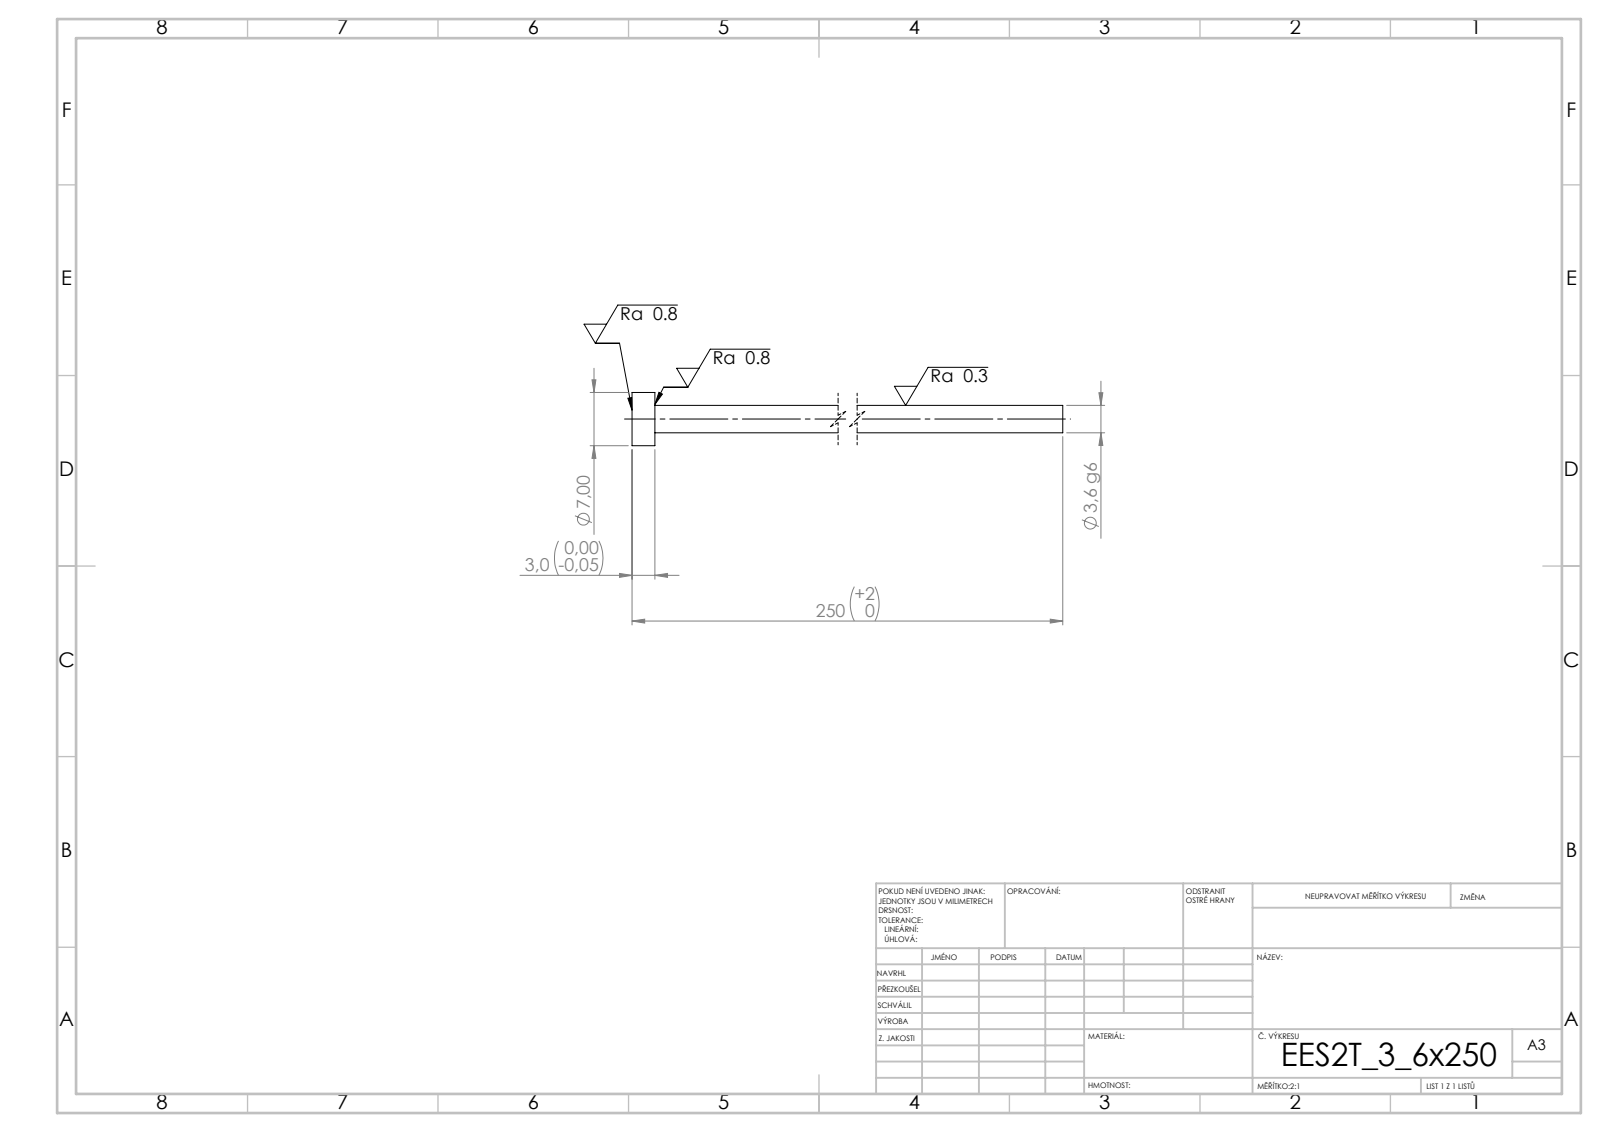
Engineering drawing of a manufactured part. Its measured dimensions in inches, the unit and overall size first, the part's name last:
Units: inches
Overall size (bounding box): 9.843 × 0.276 × 0.276
Round bosses / shafts (diameter × count): ⌀0.276 ×1, ⌀0.142 ×1
Main face-to-face distances: 0.118, 9.843, 9.724
Volume: 0.16 in³ · Surface area: 4.551 in²
Bodies: 1 solid, 7 faces (3 planar, 4 cylindrical, 0 other)
STEP written by: SolidWorks 2019 (CONFIG_CONTROL_DESIGN)
